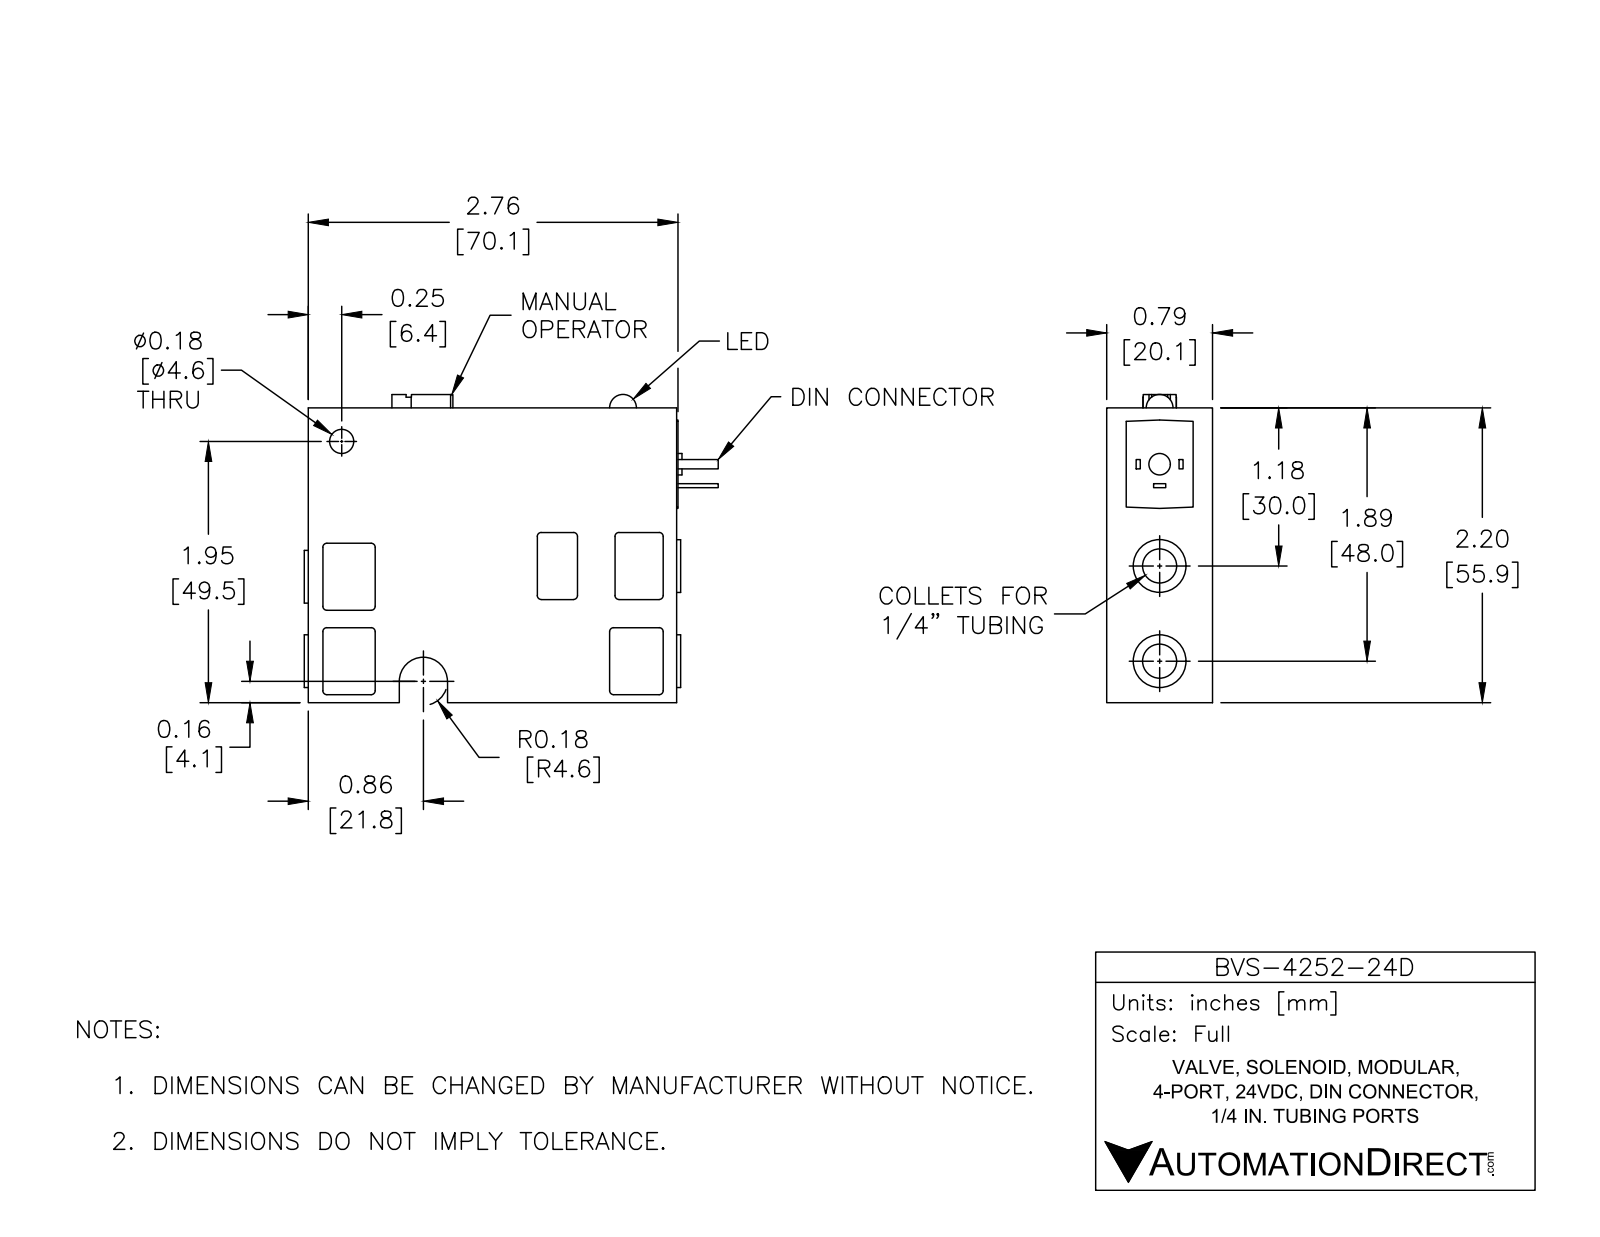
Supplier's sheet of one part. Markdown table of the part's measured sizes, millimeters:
| quantity | value |
| --- | --- |
| part name | BVS-4252-24D |
| STEP written by | SolidWorks 2016 (AUTOMOTIVE_DESIGN) |
| units | millimeters |
| bodies | 1 solid, 169 faces (99 planar, 68 cylindrical, 2 other) |
| overall size | 78.5 × 58.4 × 20.1 |
| volume | 71 680 mm³ |
| surface area | 16 250 mm² |
| round holes (diameter × count) | 6.5 × 3, 2.5 × 1, 4.6 × 1 |
| round bosses / shafts (diameter × count) | 10 × 3, 4.1 × 1 |
| partial cylindrical surfaces (radius × count) | 0.8 × 20, 0.5 × 2, 3.2 × 1, 4.6 × 1 |
| main face-to-face distances | 20.1, 2.5, 55.9, 17.5, 69.9, 15, 12.7, 2.8, 67.3, 0.8 |
| hole center spacings | 2, 14, 16, 16, 18, 32 |
